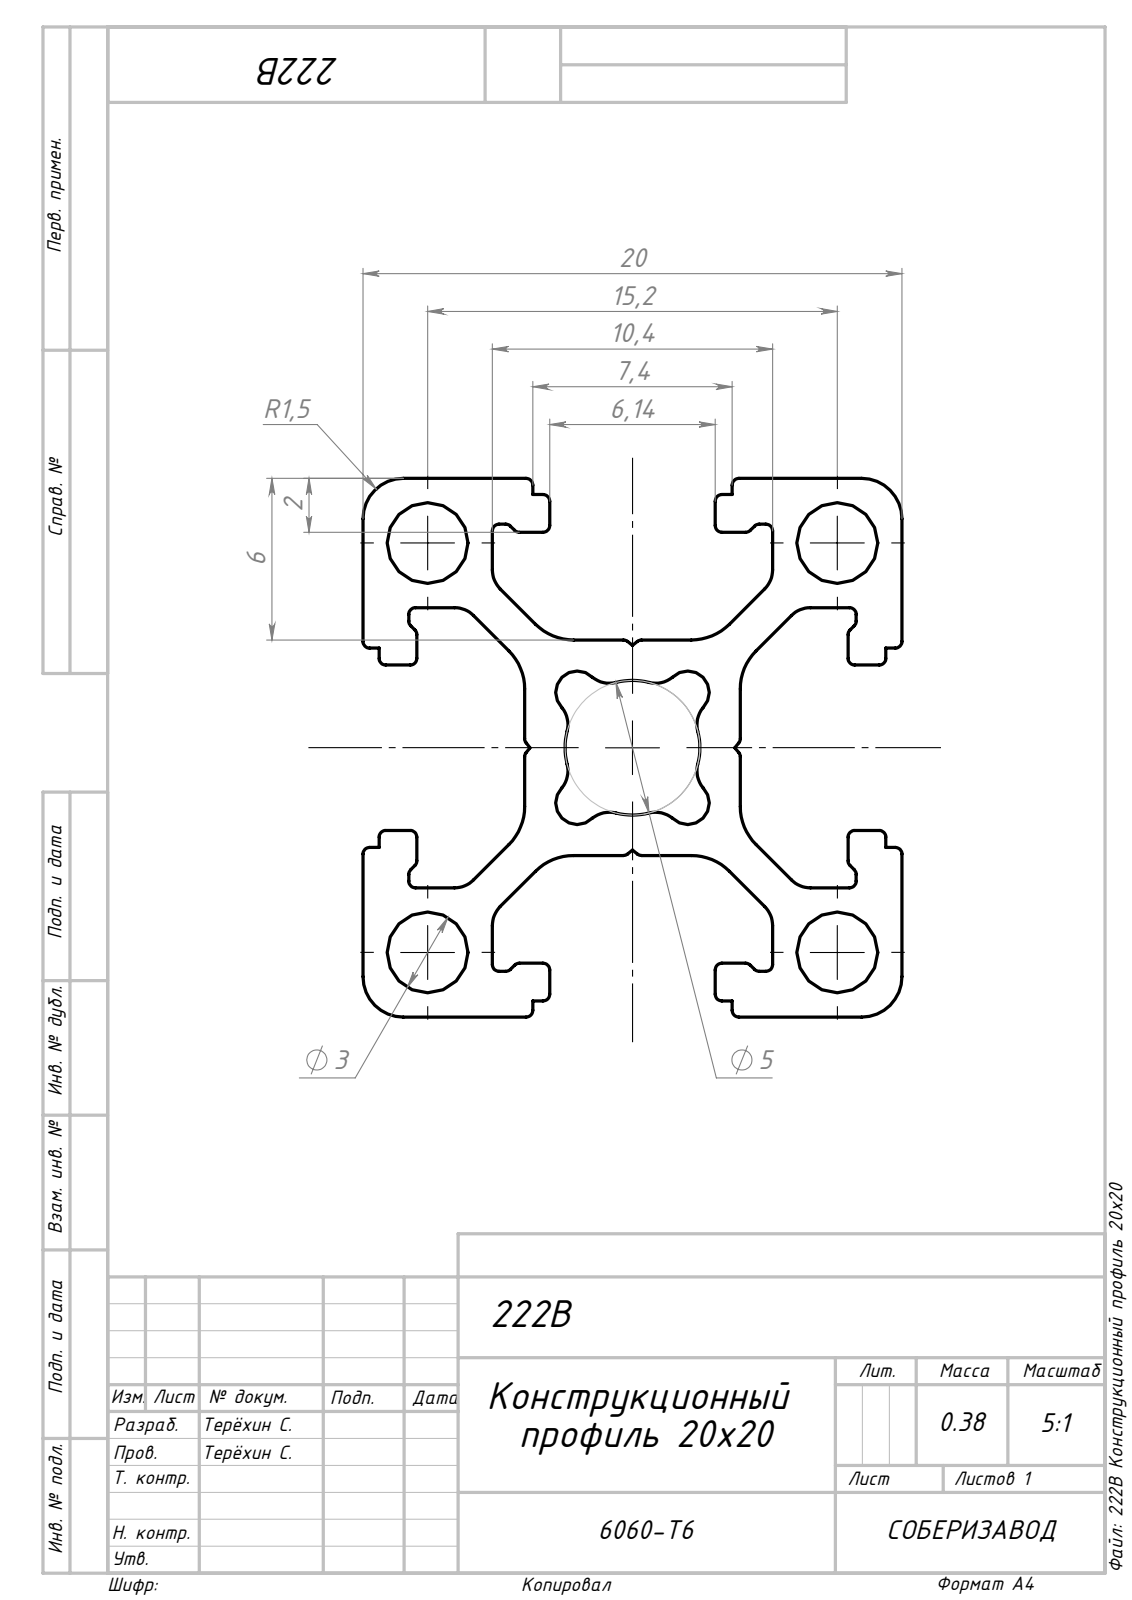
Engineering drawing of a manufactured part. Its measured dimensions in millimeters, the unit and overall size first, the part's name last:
Units: millimetres
Overall size (bounding box): 1000 × 20 × 20
Round holes (diameter × count): ⌀3 ×4
Partial cylindrical surfaces — rounded edges, fillets, slot ends (radius × count): R0.25 ×56, R1 ×16, R2 ×8, R0.8 ×4, R1.5 ×4, R2.5 ×1
Main face-to-face distances: 20, 6, 14, 4.8, 15.2, 1.2, 9.2, 1.4, 12, 8
Hole centre spacings: 15.2, 21.5
Volume: 142 104 mm³ · Surface area: 208 901 mm²
Bodies: 1 solid, 195 faces (90 planar, 105 cylindrical, 0 other)
Part name (STEP PRODUCT): Сборка1; 222B Конструкционный профиль 20х20_00
STEP written by: SolidWorks 2024 (AUTOMOTIVE_DESIGN)
